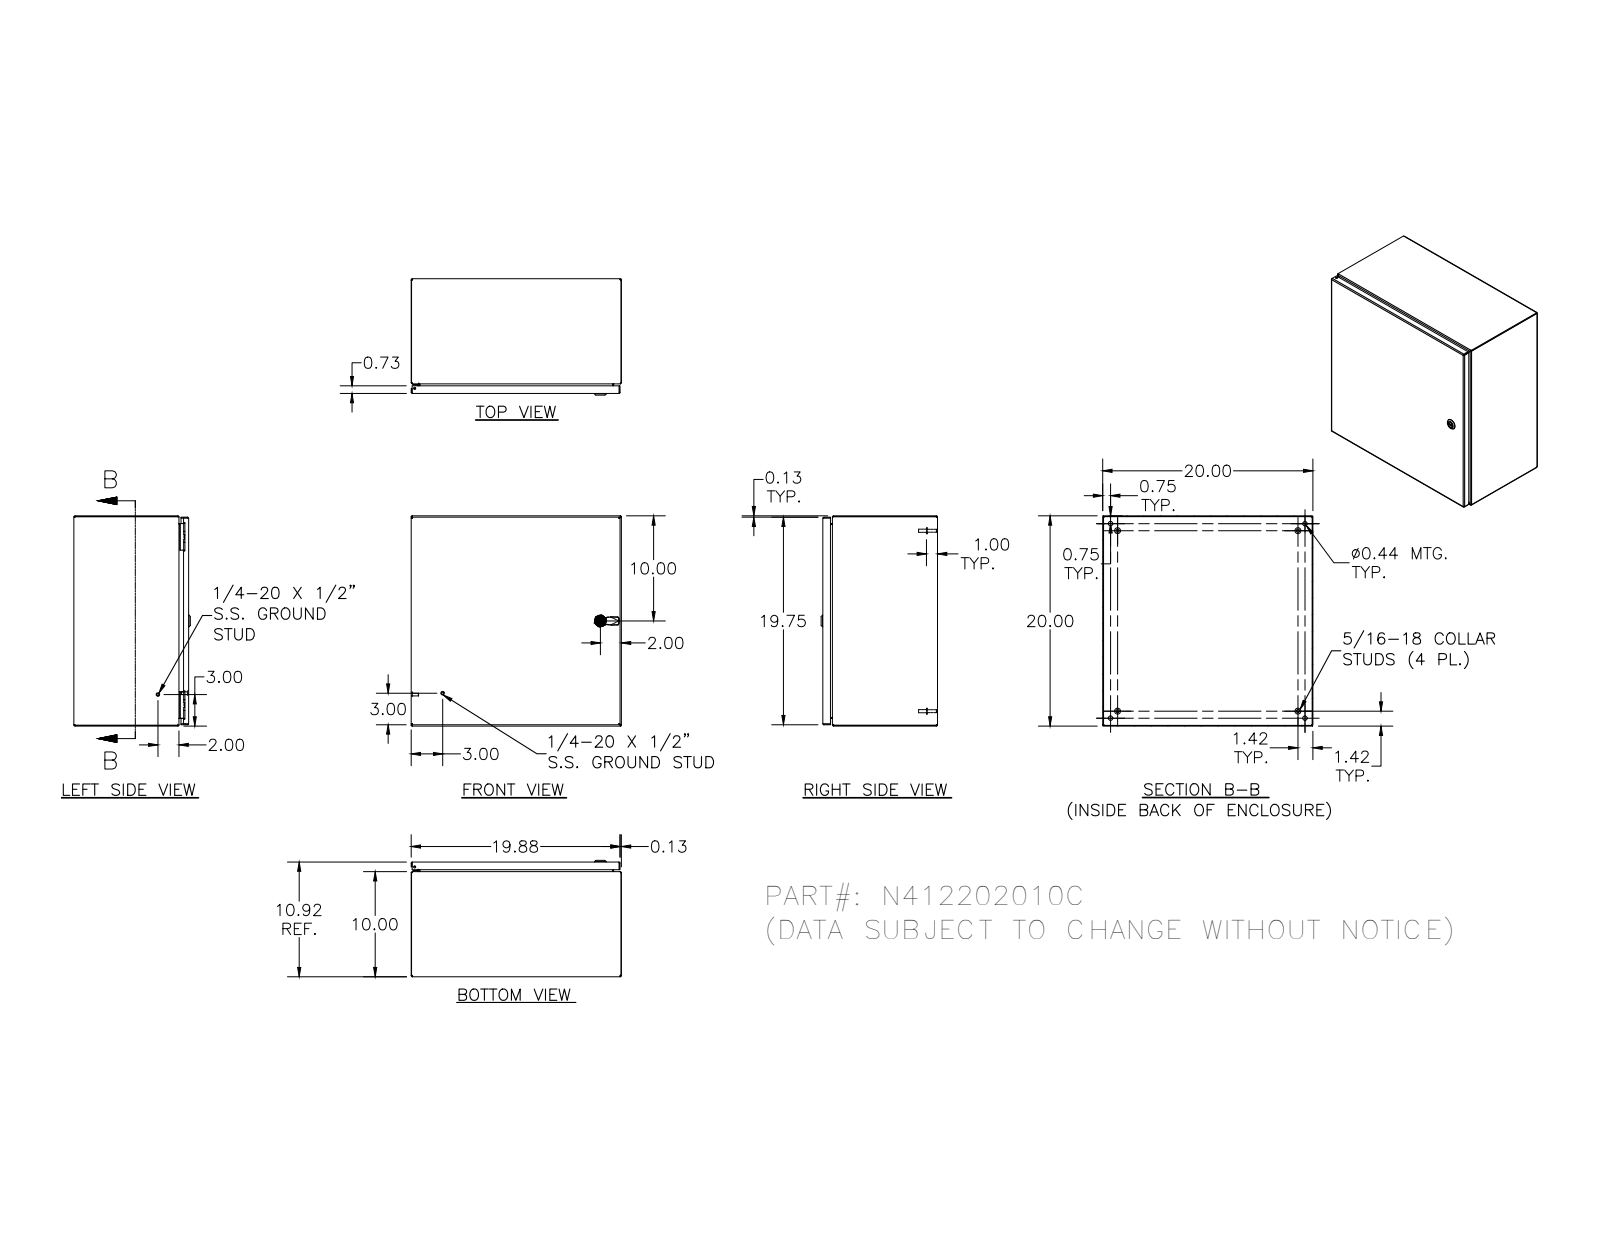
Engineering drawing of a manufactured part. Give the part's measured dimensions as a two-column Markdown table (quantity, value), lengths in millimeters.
| quantity | value |
| --- | --- |
| part name | N412202010C |
| STEP written by | SolidWorks 2018 (AUTOMOTIVE_DESIGN) |
| units | millimeters |
| bodies | 33 solids, 1449 faces (530 planar, 547 cylindrical, 372 other) |
| overall size | 508 × 508 × 281.3 |
| volume | 2 137 000 mm³ |
| surface area | 2 286 000 mm² |
| round holes (diameter × count) | 4.8 × 5, 2.4 × 4, 3.9 × 4, 4.2 × 4, 4.4 × 4, 11.1 × 4, 4 × 2, 4.7 × 1, 5 × 1, 8 × 1, 10 × 1, 10.2 × 1 |
| round bosses / shafts (diameter × count) | 6.4 × 10, 3.3 × 5, 14.3 × 4, 9.1 × 4, 8.1 × 4, 7.6 × 4, 7 × 4, 6.5 × 4 |
| partial cylindrical surfaces (radius × count) | 0.3 × 30, 0.8 × 30, 1.3 × 26, 2.7 × 20, 0.4 × 18, 3.2 × 16, 0.5 × 13, 0.8 × 8 |
| main face-to-face distances | 1.9, 275.4, 506.1, 504.2, 506.1, 508, 1.9, 273.5, 277.3, 23.3 |
| hole center spacings | 406.4, 16.8, 16.7, 33.2, 49.9, 389.6, 423.2, 469.9 |
